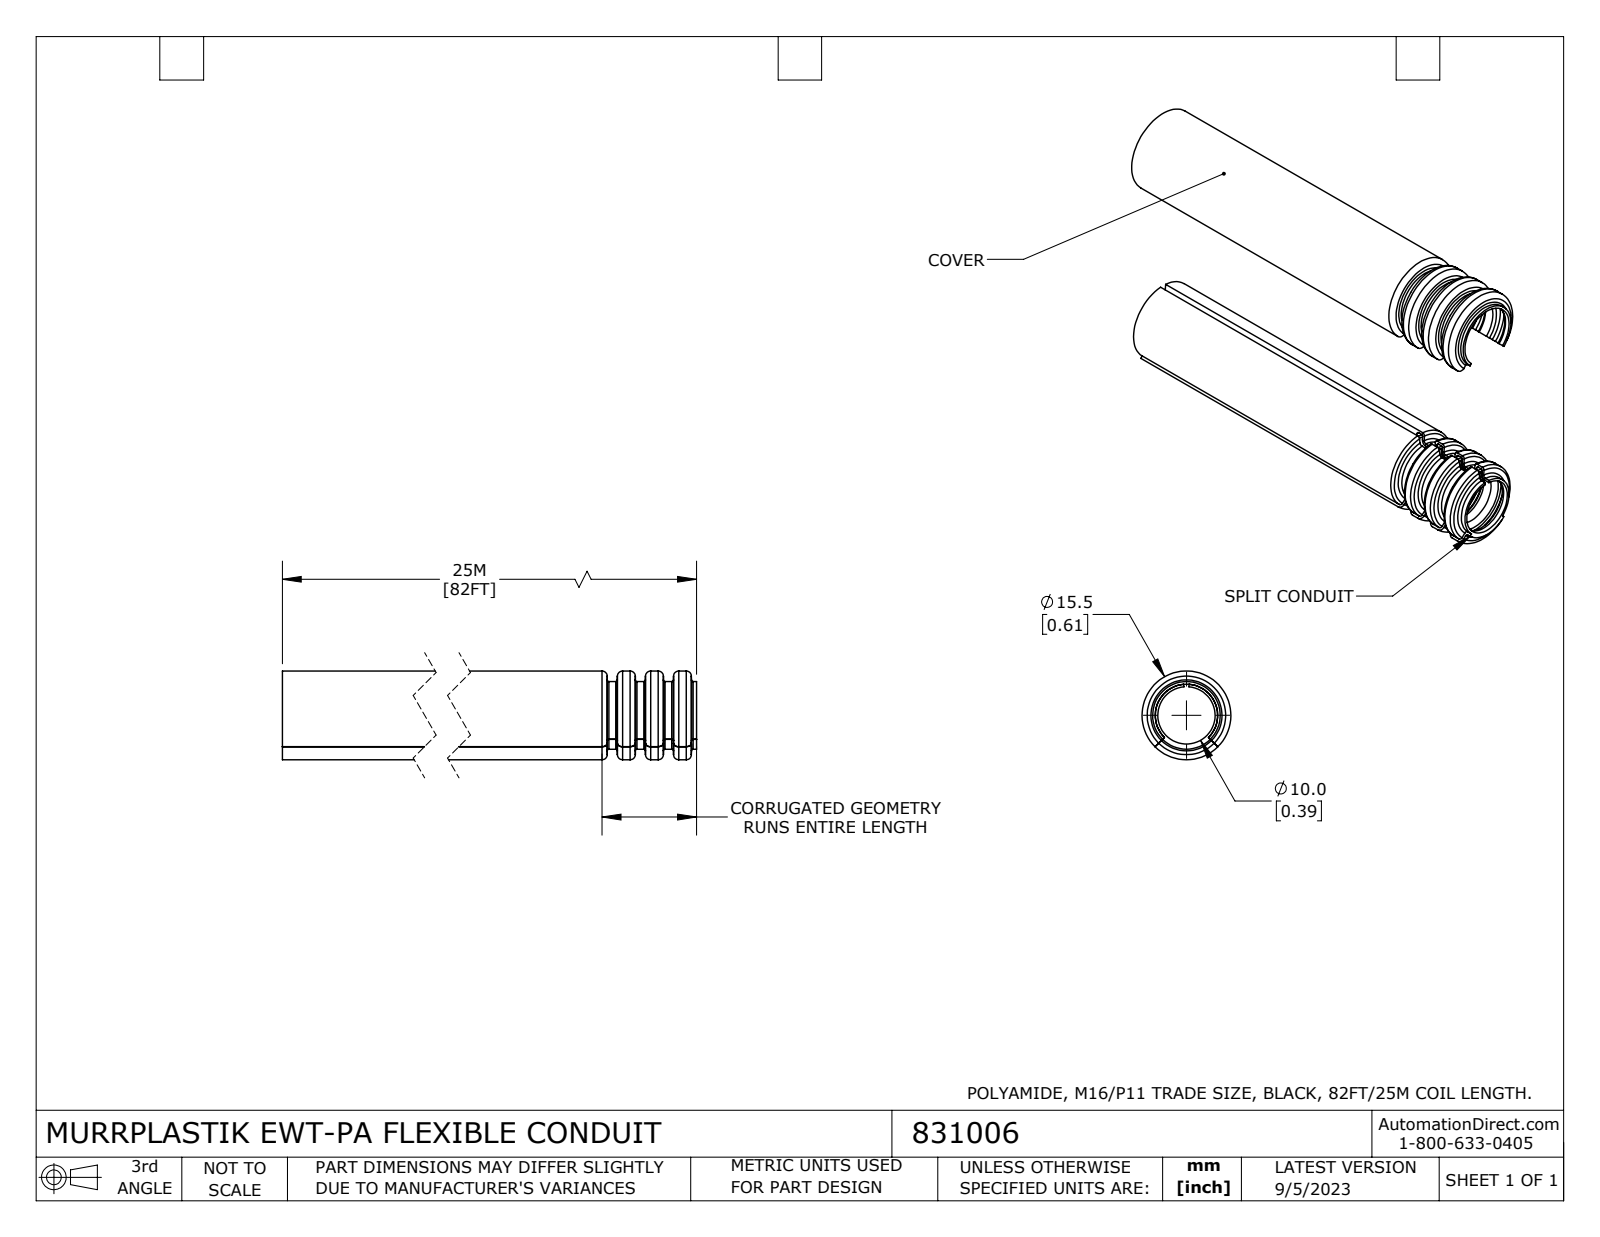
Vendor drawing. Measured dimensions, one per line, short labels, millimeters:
name: 831006
written by: SolidWorks 2021 (CONFIG_CONTROL_DESIGN)
unit: mm
bodies: 2 solids, 339 faces (10 planar, 107 cylindrical, 222 other)
size: 80 × 15.5 × 15.5
volume: 7 690 mm³; area: 13 560 mm²
holes: 1× ⌀10, 1× ⌀13.7
bosses: 1× ⌀15.5, 1× ⌀11.8
rounds: 1× R5.5, 1× R7.3
face distances: 80
